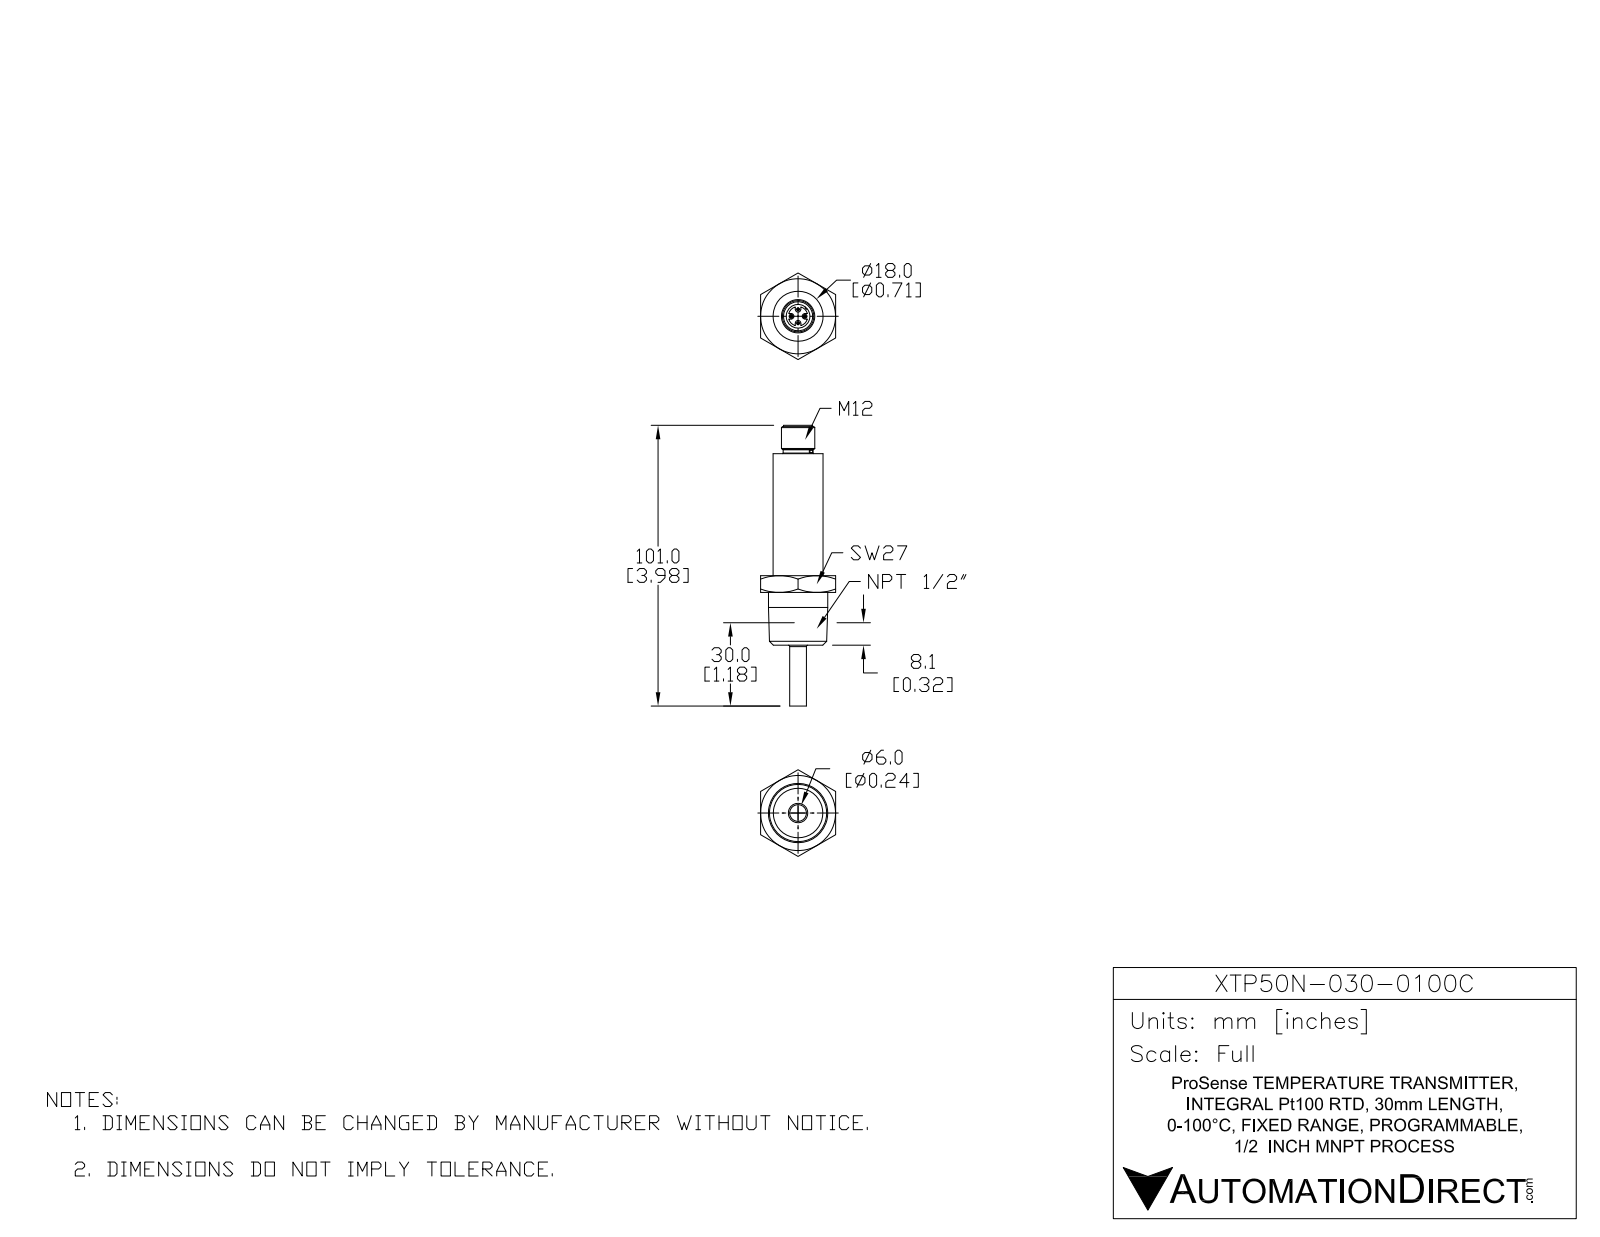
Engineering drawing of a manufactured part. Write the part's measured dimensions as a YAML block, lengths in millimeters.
part_name: "XTP50N-030-0100C"
step_written_by: "SolidWorks 2015 (AUTOMOTIVE_DESIGN)"
units: millimeters
bodies: {solids: 1, faces: 117, planar: 43, cylindrical: 34, other: 40}
overall_size: [101, 31.18, 27]
volume: 22355
surface_area: 6897
round_holes:
  - {diameter: 4, count: 1}
  - {diameter: 8.5, count: 1}
round_bosses_or_shafts:
  - {diameter: 1.02, count: 4}
  - {diameter: 21.34, count: 1}
  - {diameter: 18, count: 1}
  - {diameter: 12, count: 1}
  - {diameter: 10.7, count: 1}
  - {diameter: 10.5, count: 1}
  - {diameter: 6, count: 1}
partial_cylinders:
  - {radius: 1, count: 4}
  - {radius: 3.5, count: 1}
  - {radius: 4.25, count: 1}
face_to_face_distances: [27, 25, 19, 6, 68.9, 49.9, 43.9, 79.1, 60.1, 54.1]
